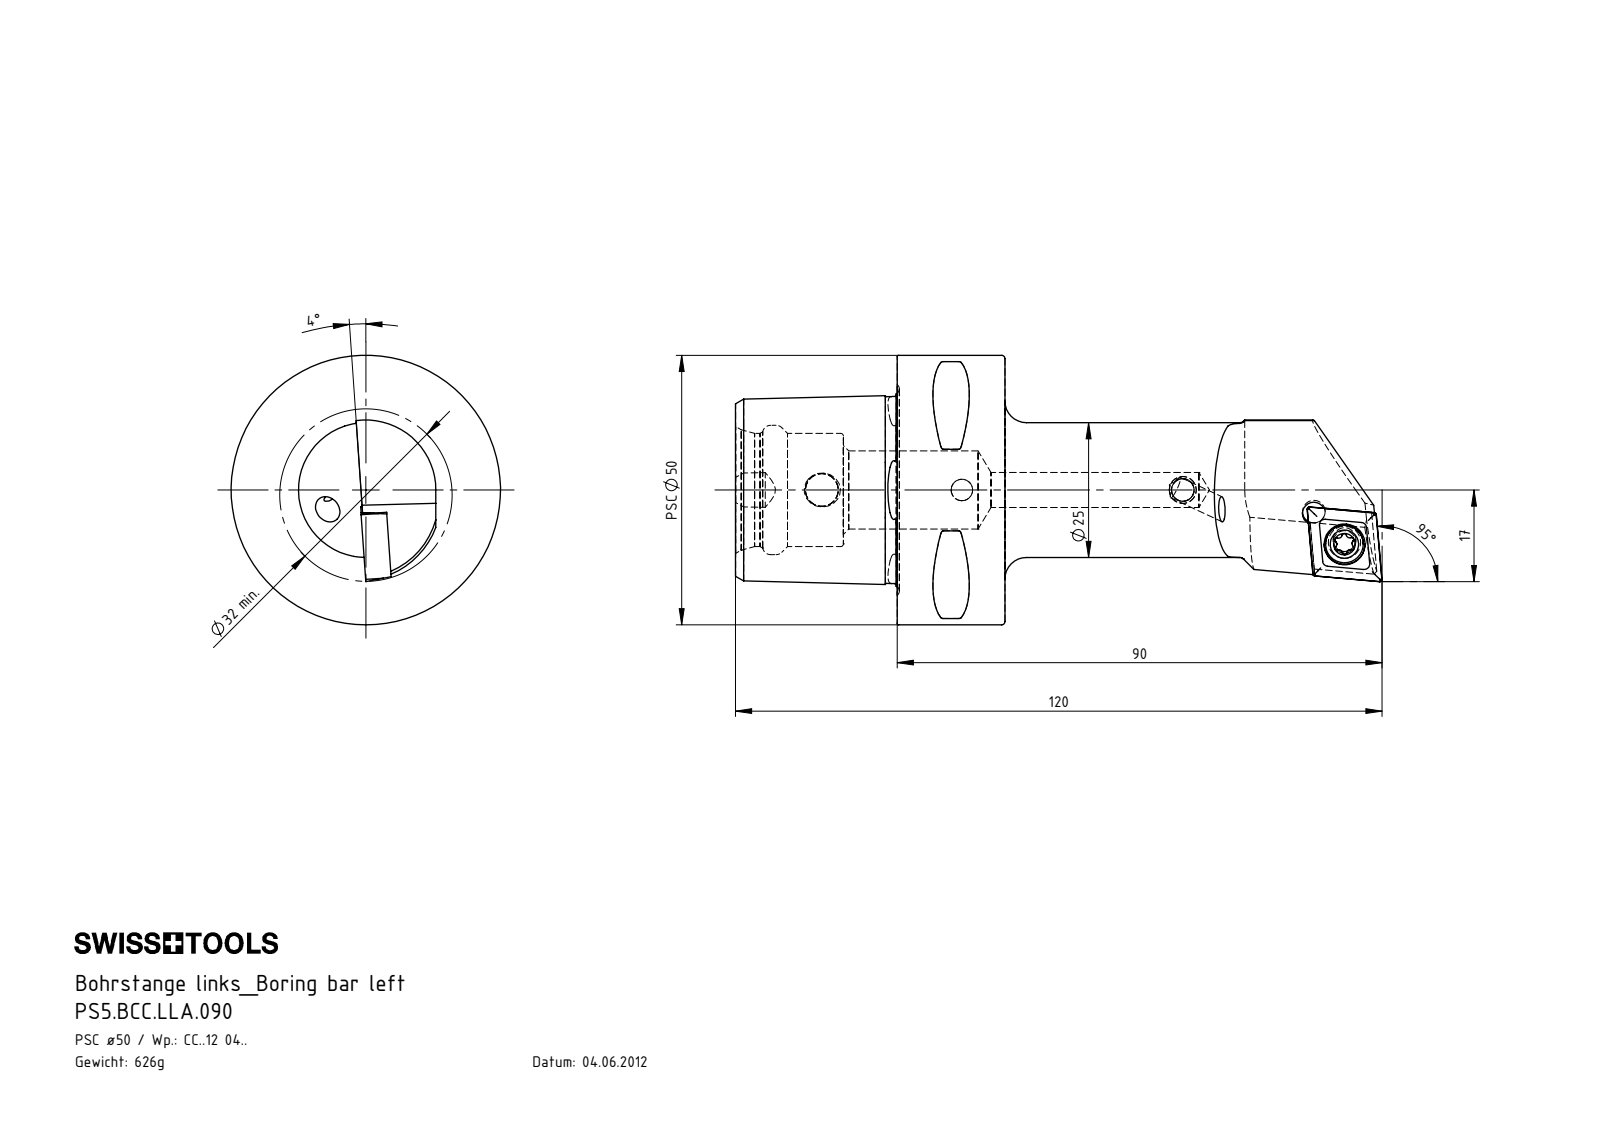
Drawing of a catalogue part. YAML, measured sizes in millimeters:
part_name: "KVT_MB_600_050; PS5-BCC.LLA.090_A; PS5.BCC.LLA.090; CCMT120404 (+1 more)"
step_written_by: "SolidWorks 2017 (AUTOMOTIVE_DESIGN)"
units: millimeters
bodies: {solids: 5, faces: 280, planar: 49, cylindrical: 75, other: 156}
overall_size: [120, 50, 50]
volume: 79796
surface_area: 19989
round_holes:
  - {diameter: 4.2, count: 4}
  - {diameter: 4, count: 2}
  - {diameter: 5.5, count: 1}
  - {diameter: 6.1, count: 1}
  - {diameter: 6.5, count: 1}
  - {diameter: 7.6, count: 1}
  - {diameter: 14.5, count: 1}
  - {diameter: 21, count: 1}
  - {diameter: 24, count: 1}
round_bosses_or_shafts:
  - {diameter: 5, count: 2}
  - {diameter: 50, count: 1}
  - {diameter: 25, count: 1}
  - {diameter: 7, count: 1}
partial_cylinders:
  - {radius: 0.5, count: 8}
  - {radius: 0.39, count: 6}
  - {radius: 0.69, count: 3}
  - {radius: 0.69, count: 3}
  - {radius: 3, count: 1}
  - {radius: 4, count: 1}
  - {radius: 13, count: 1}
  - {radius: 15, count: 1}
face_to_face_distances: [20, 30, 50, 4.46, 19.18, 44.4, 10, 29.8, 9.8, 20.2]
hole_center_spacings: [8.04, 8.09, 26, 41, 67]
